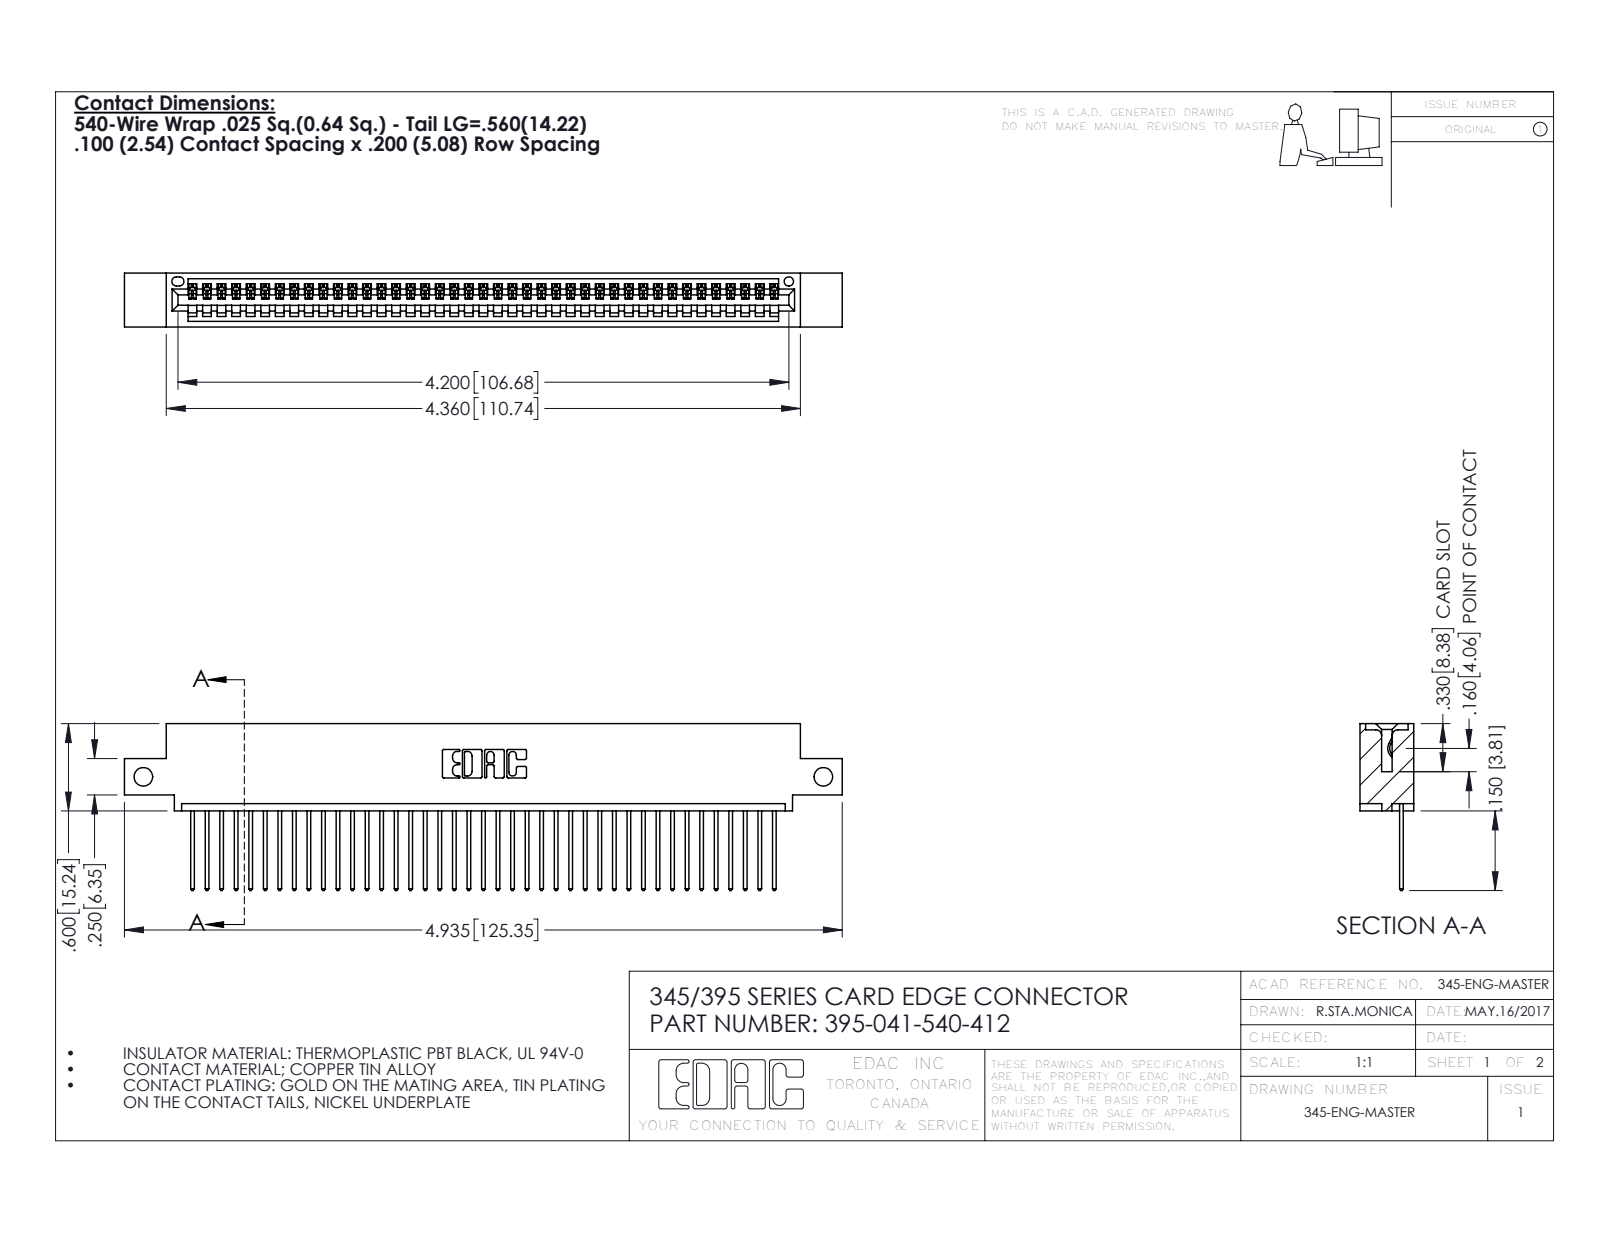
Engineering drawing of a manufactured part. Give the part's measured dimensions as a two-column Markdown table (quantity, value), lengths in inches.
| quantity | value |
| --- | --- |
| part name | 395-041-540-412; 345 Part_0.110 Offset - Side Mount; 345-292-001_345-293-140 |
| STEP written by | SolidWorks 2016 (CONFIG_CONTROL_DESIGN) |
| units | inches |
| bodies | 42 solids, 2508 faces (1724 planar, 784 cylindrical, 0 other) |
| overall size | 4.935 × 1.147 × 0.37 |
| volume | 0.72 in³ |
| surface area | 24.8 in² |
| round holes (diameter × count) | 0.128 × 2, 0.064 × 1 |
| partial cylindrical surfaces (radius × count) | 0.006 × 82, 0.01 × 82, 0.01 × 22, 0.007 × 6, 0.031 × 6, 0.026 × 3, 0.031 × 2, 0.04 × 2 |
| main face-to-face distances | 0.298, 0.072, 0.37, 0.098, 0.272, 0.025, 0.2, 0.225, 0.149, 0.072 |
| hole center spacings | 4.675 |
